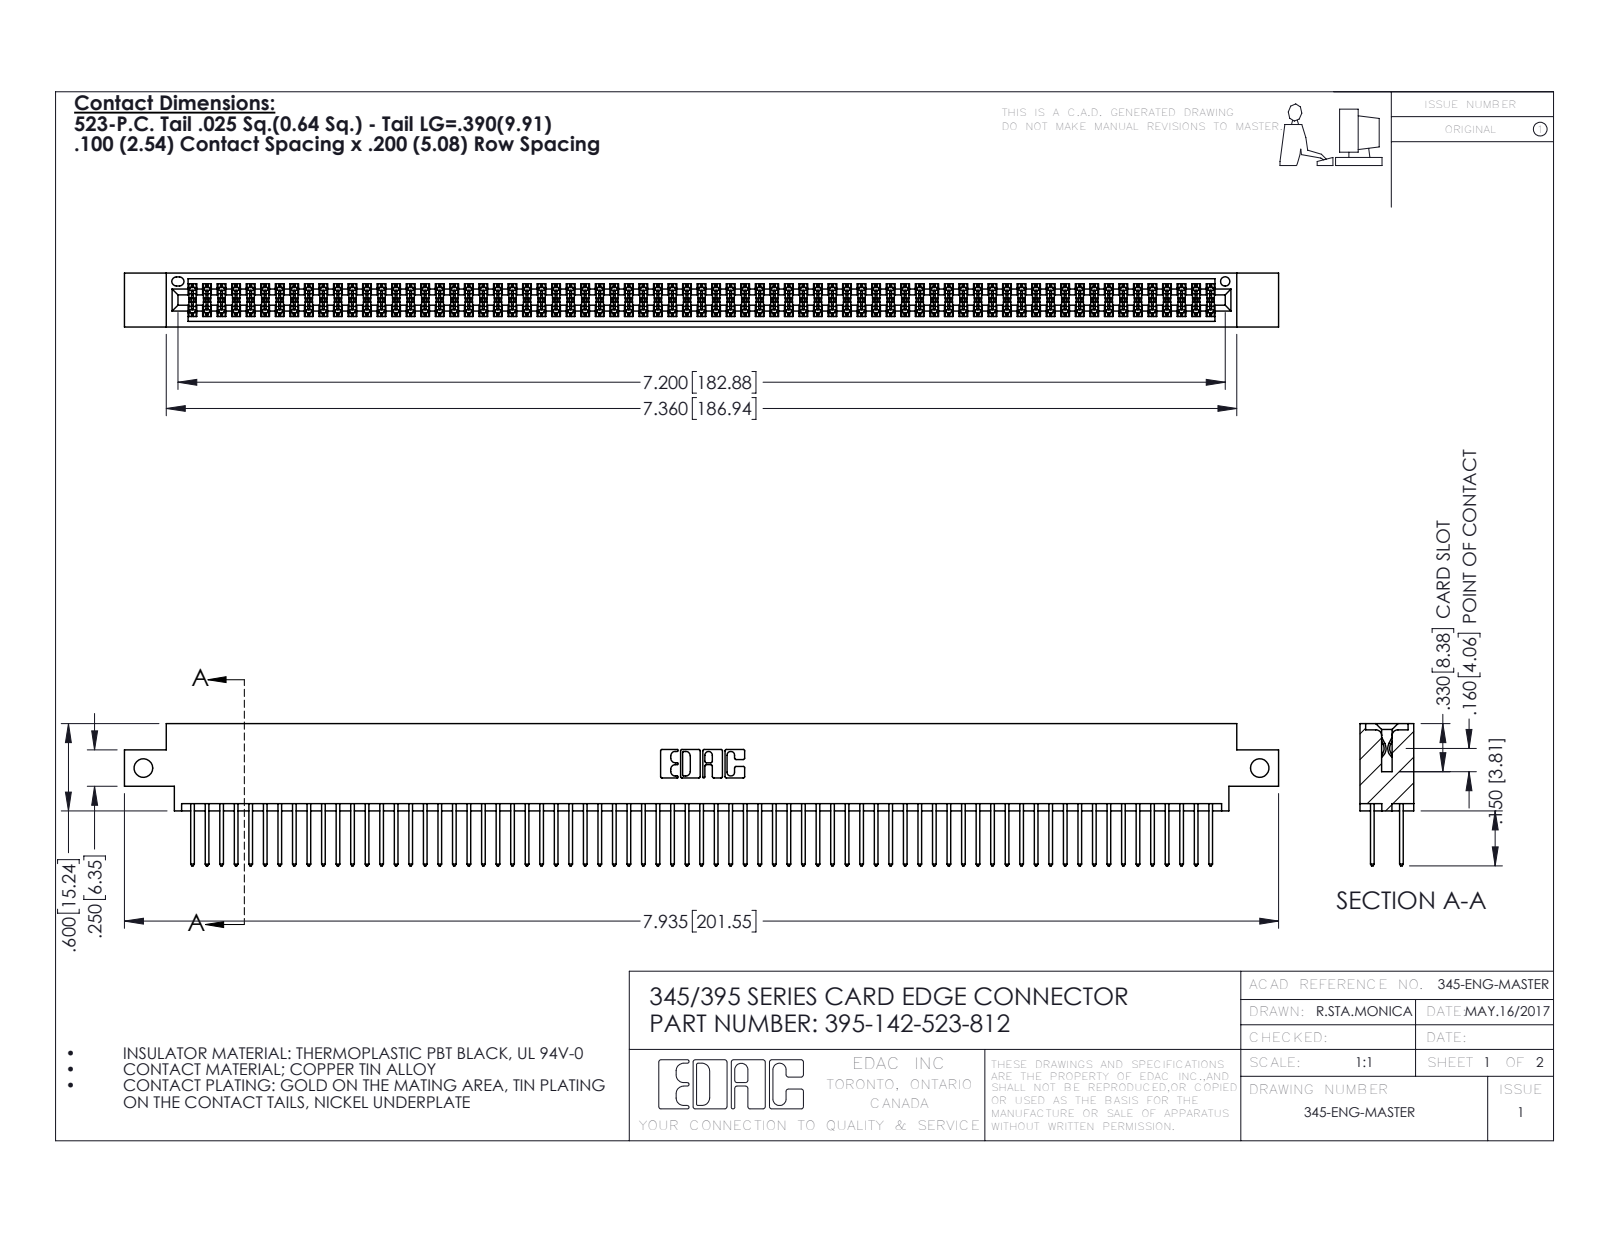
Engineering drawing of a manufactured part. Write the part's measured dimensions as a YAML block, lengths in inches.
part_name: "345 Part_0.170 Offset - Side Mount; 345-292-001_345-293-123; 395-142-523-812"
step_written_by: "SolidWorks 2016 (CONFIG_CONTROL_DESIGN)"
units: inches
bodies: {solids: 143, faces: 7230, planar: 4770, cylindrical: 2460, other: 0}
overall_size: [7.935, 0.977, 0.37]
volume: 1.217
surface_area: 48.59
round_holes:
  - {diameter: 0.128, count: 2}
  - {diameter: 0.064, count: 1}
partial_cylinders:
  - {radius: 0.006, count: 213}
  - {radius: 0.01, count: 142}
  - {radius: 0.01, count: 22}
  - {radius: 0.007, count: 6}
  - {radius: 0.031, count: 6}
  - {radius: 0.026, count: 3}
  - {radius: 0.014, count: 2}
  - {radius: 0.019, count: 2}
face_to_face_distances: [0.072, 0.298, 0.2, 0.098, 0.272, 0.025, 0.37, 0.225, 0.175, 0.149]
hole_center_spacings: [7.675]
